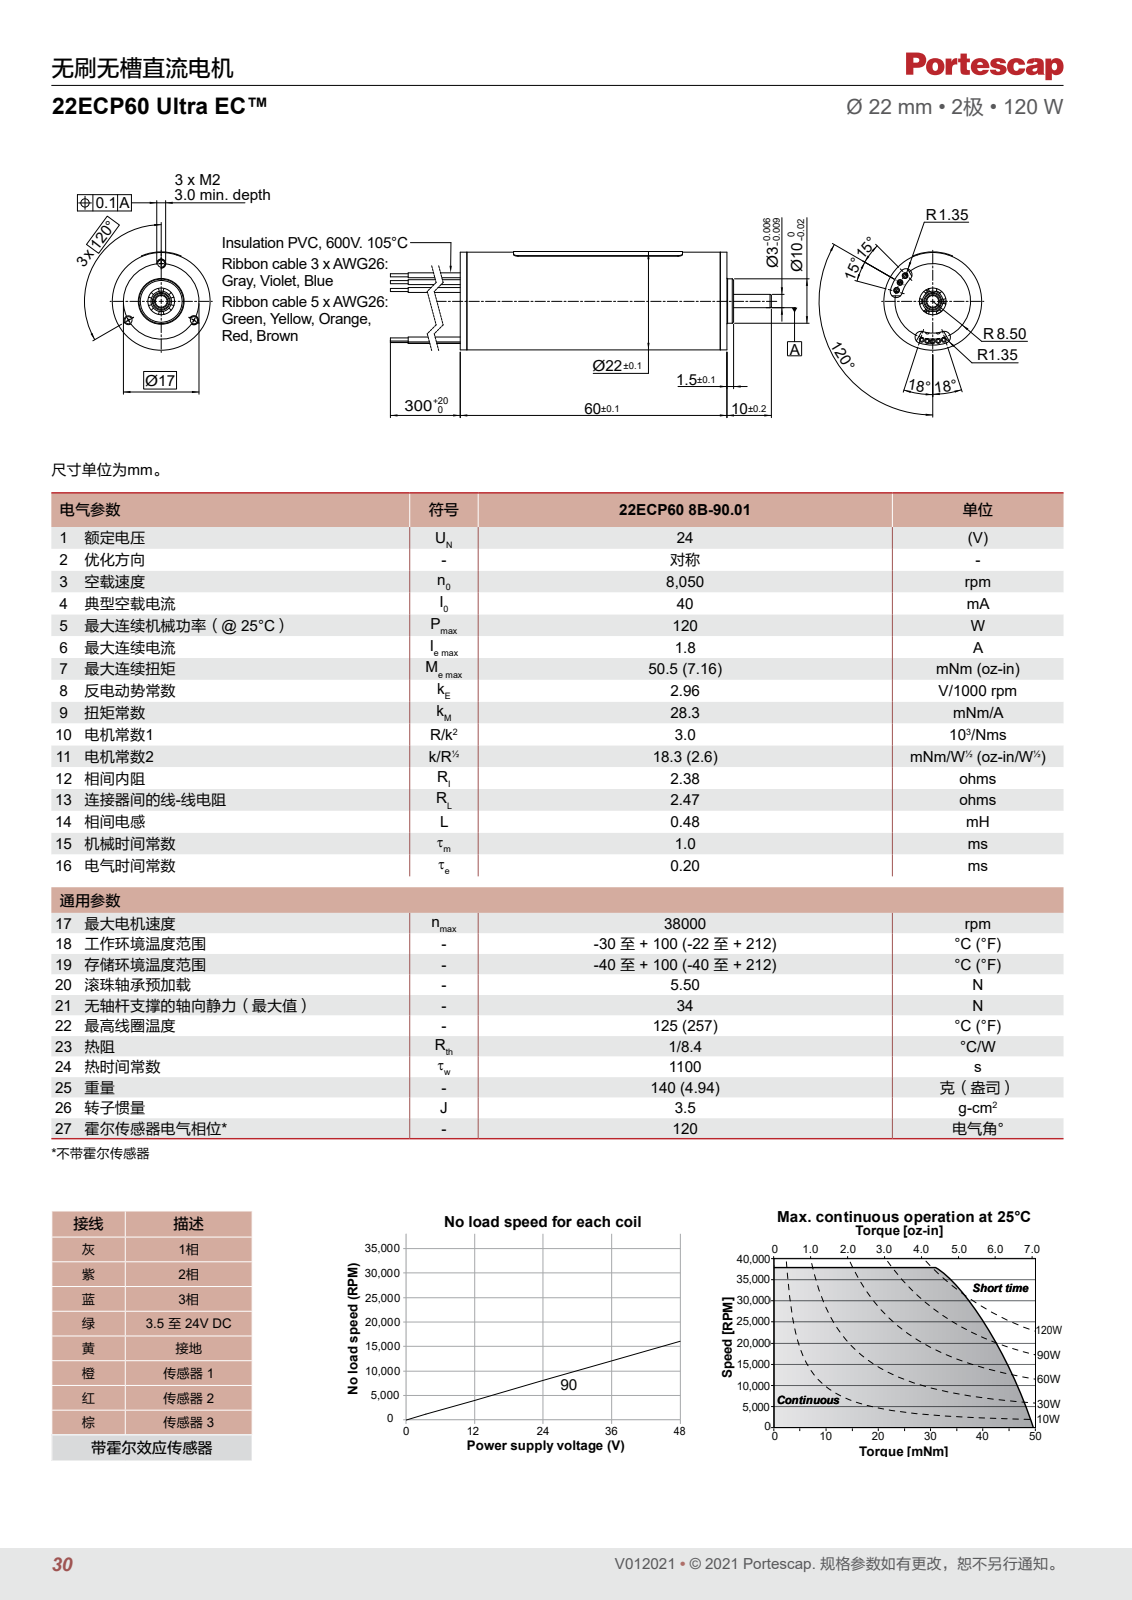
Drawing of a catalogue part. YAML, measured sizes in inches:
part_name: "22ECP60"
step_written_by: "SolidWorks 2010 (CONFIG_CONTROL_DESIGN)"
units: inches
bodies: {solids: 1, faces: 140, planar: 35, cylindrical: 75, other: 30}
overall_size: [14.661, 0.872, 0.866]
volume: 1.536
surface_area: 21.25
round_holes:
  - {diameter: 0.063, count: 3}
  - {diameter: 0.236, count: 1}
  - {diameter: 0.252, count: 1}
  - {diameter: 0.315, count: 1}
round_bosses_or_shafts:
  - {diameter: 0.043, count: 8}
  - {diameter: 0.028, count: 8}
  - {diameter: 0.866, count: 1}
  - {diameter: 0.394, count: 1}
  - {diameter: 0.181, count: 1}
  - {diameter: 0.118, count: 1}
partial_cylinders:
  - {radius: 0.039, count: 4}
  - {radius: 0.053, count: 4}
  - {radius: 0.281, count: 1}
  - {radius: 0.388, count: 1}
  - {radius: 0.439, count: 1}
face_to_face_distances: [2.362, 0.068, 2.294, 0.039, 2.421, 2.353, 0.059, 0.029, 2.323, 2.382]
hole_center_spacings: [0.335, 0.58]
